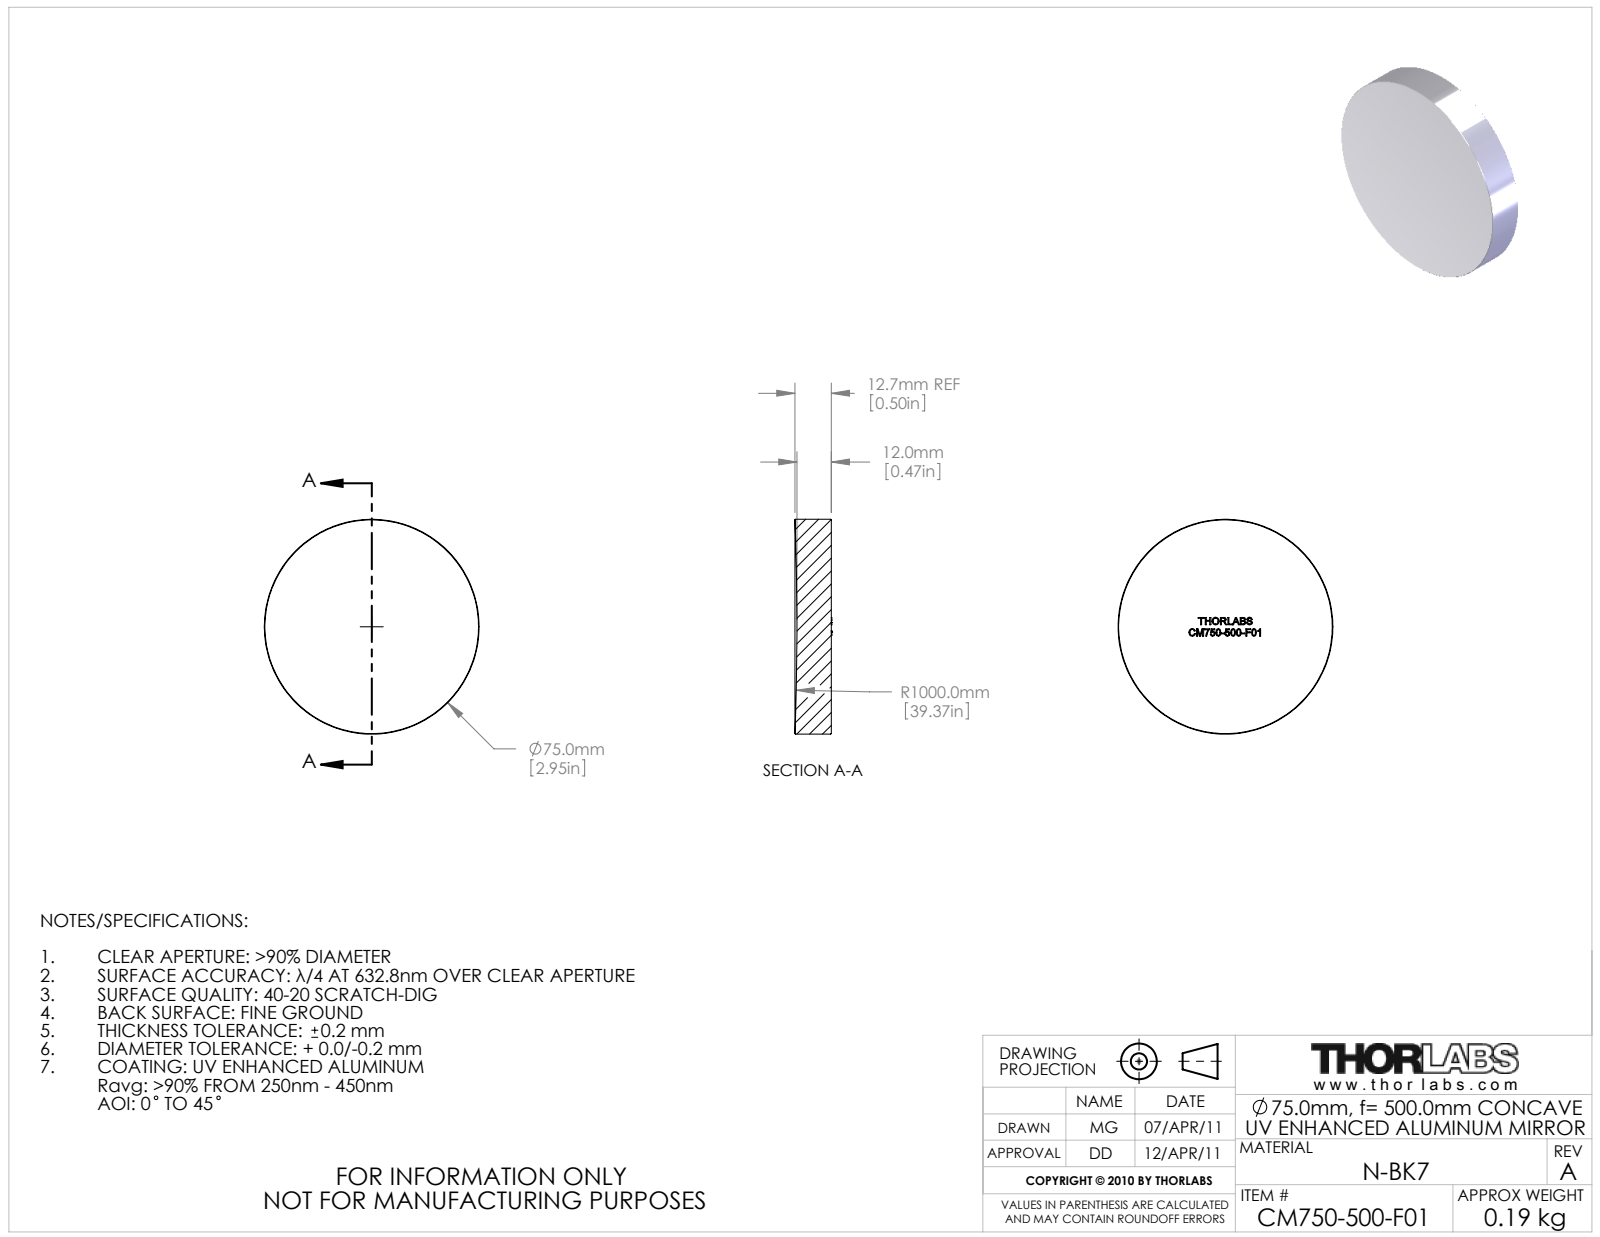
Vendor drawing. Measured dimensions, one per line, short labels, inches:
name: 22205-E0W
written by: SolidWorks 2011 (AUTOMOTIVE_DESIGN)
unit: in
bodies: 1 solid, 270 faces (147 planar, 2 cylindrical, 121 other)
size: 2.953 × 2.953 × 0.5
volume: 3.329 in³; area: 18.25 in²
bosses: 1× ⌀2.953
face distances: 0.101, 0.014, 0.015, 0.248, 0.156, 0.057, 0.062, 0.544, 0.089, 0.114
